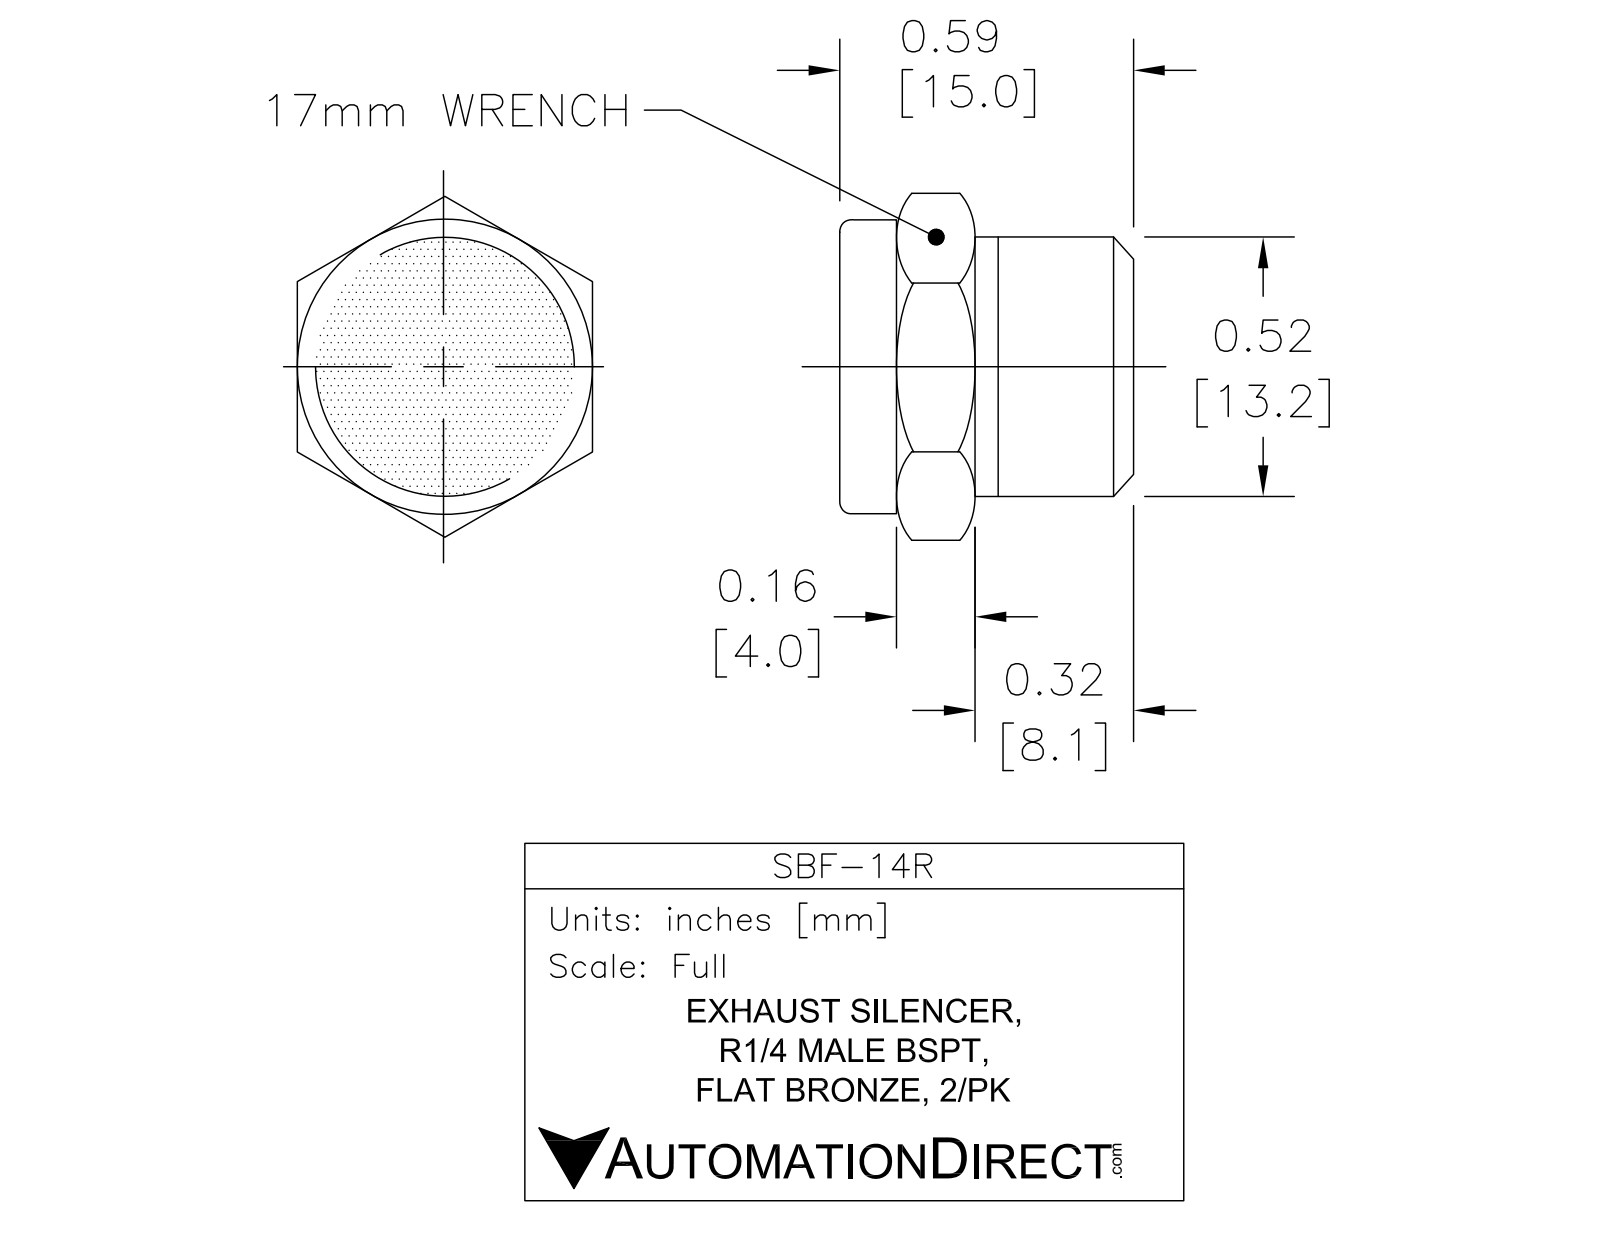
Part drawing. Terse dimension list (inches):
name: SBF-14R
written by: SolidWorks 2015 (CONFIG_CONTROL_DESIGN)
unit: in
bodies: 1 solid, 46 faces (12 planar, 15 cylindrical, 19 other)
size: 0.635 × 0.59 × 0.55
volume: 0.107 in³; area: 2.077 in²
holes: 1× ⌀0.22
bosses: 1× ⌀0.52
face distances: 0.59, 0.55, 0.55, 0.43, 0.16, 0.29, 0.14, 0.3, 0.32, 0.03
